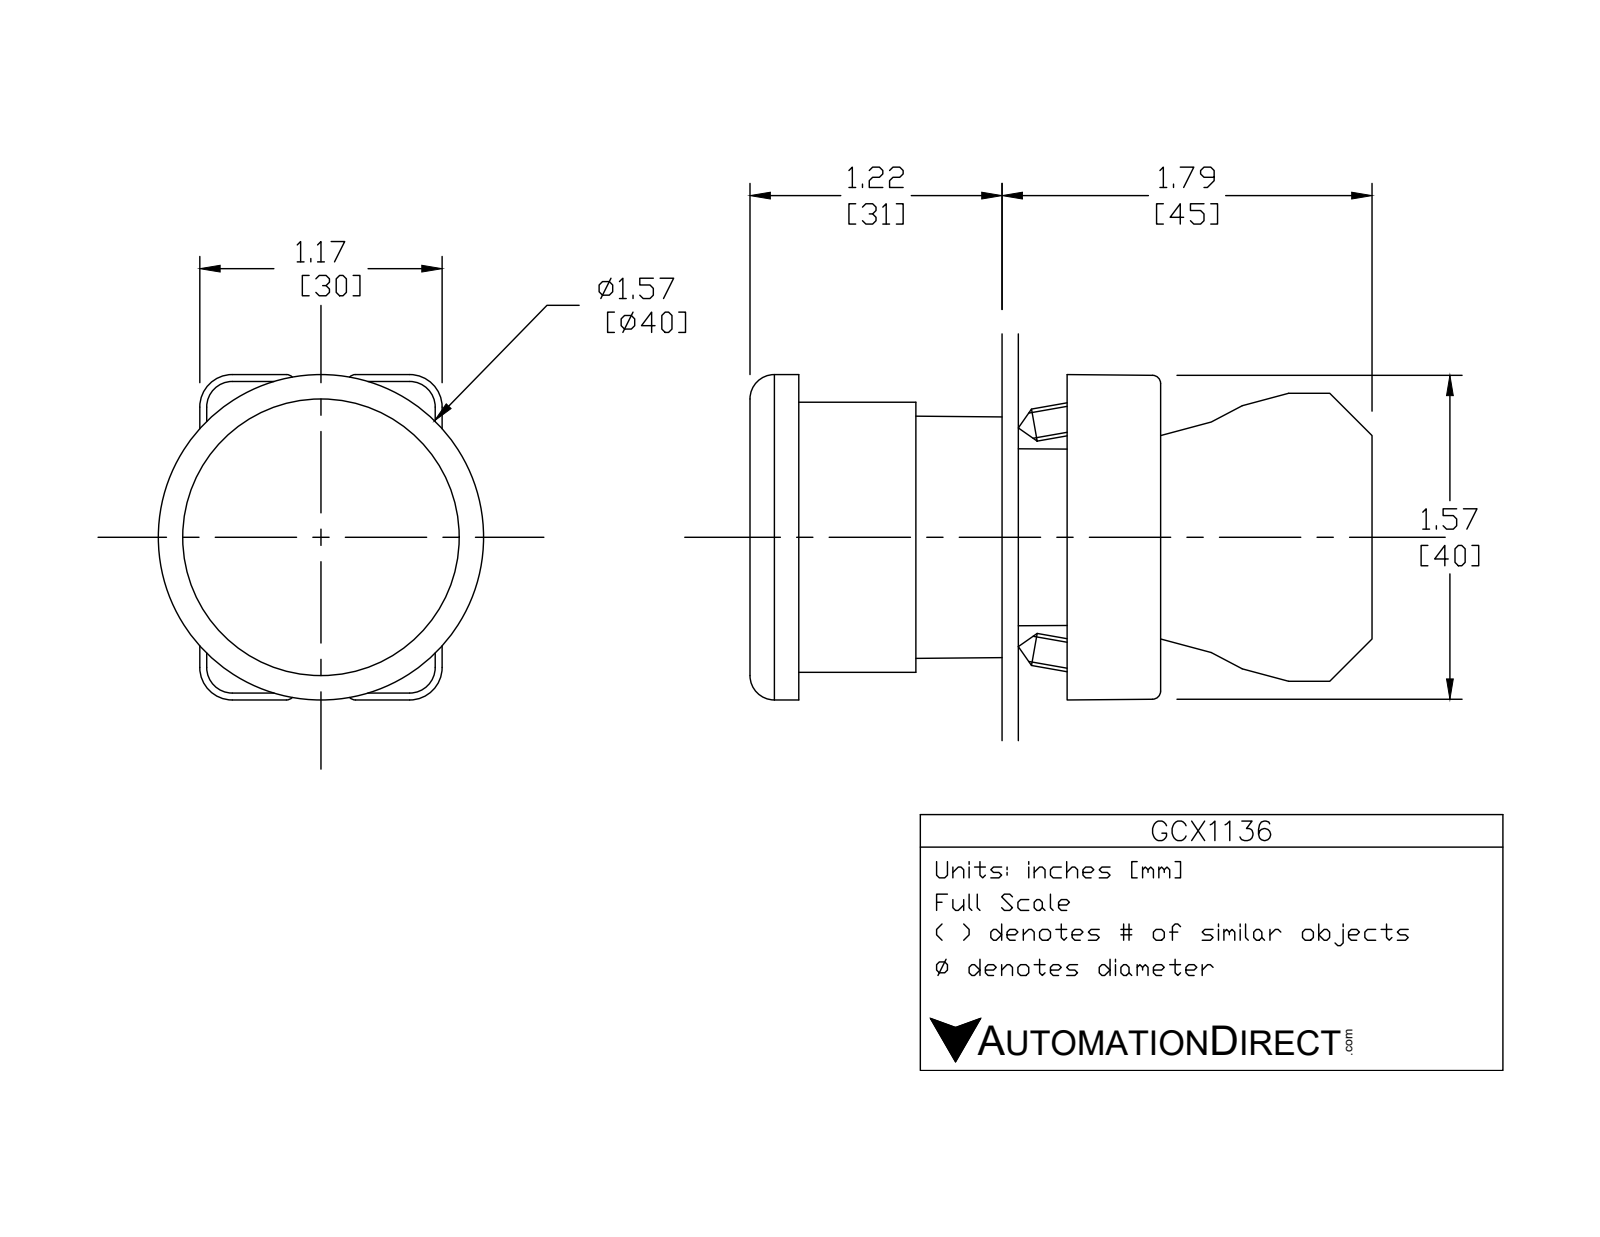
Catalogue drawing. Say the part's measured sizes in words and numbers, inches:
The part is named "ecx1030; GCX1136 OPERATOR; GCX1136; ECX1029-2". Its 3-D file was written by "SolidWorks 2016 (AUTOMOTIVE_DESIGN)". It is 6 solids with 399 faces: 230 planar, 140 cylindrical and 29 other. Overall it measures 2.954 by 2.362 by 2.362 inches. Its volume is 2.344 cubic inches and its surface area 38.83 square inches. Round holes: 2 of diameter 0.079, 2 of diameter 0.124, 2 of diameter 0.13, 1 of diameter 0.087, 1 of diameter 0.197, 1 of diameter 0.878, 1 of diameter 0.888, 1 of diameter 1.024, 1 of diameter 1.181. Round bosses or shafts: 2 of diameter 0.157, 1 of diameter 2.362, 1 of diameter 1.299, 1 of diameter 1.175, 1 of diameter 0.945, 1 of diameter 0.856, 1 of diameter 0.78. Partial cylindrical surfaces (rounded edges, fillets, slot ends): 24 of radius 0.059, 12 of radius 0.041, 12 of radius 0.124, 12 of radius 0.157, 4 of radius 0.039, 2 of radius 0.128, 1 of radius 0.02, 1 of radius 0.063. The main face-to-face distances are 0.197, 1.724, 1.921, 0.579, 0.039, 0.033, 1.763, 0.157, 0.031, 1.024. The hole center spacings are 0.236, 0.544, 0.472, 0.49.
